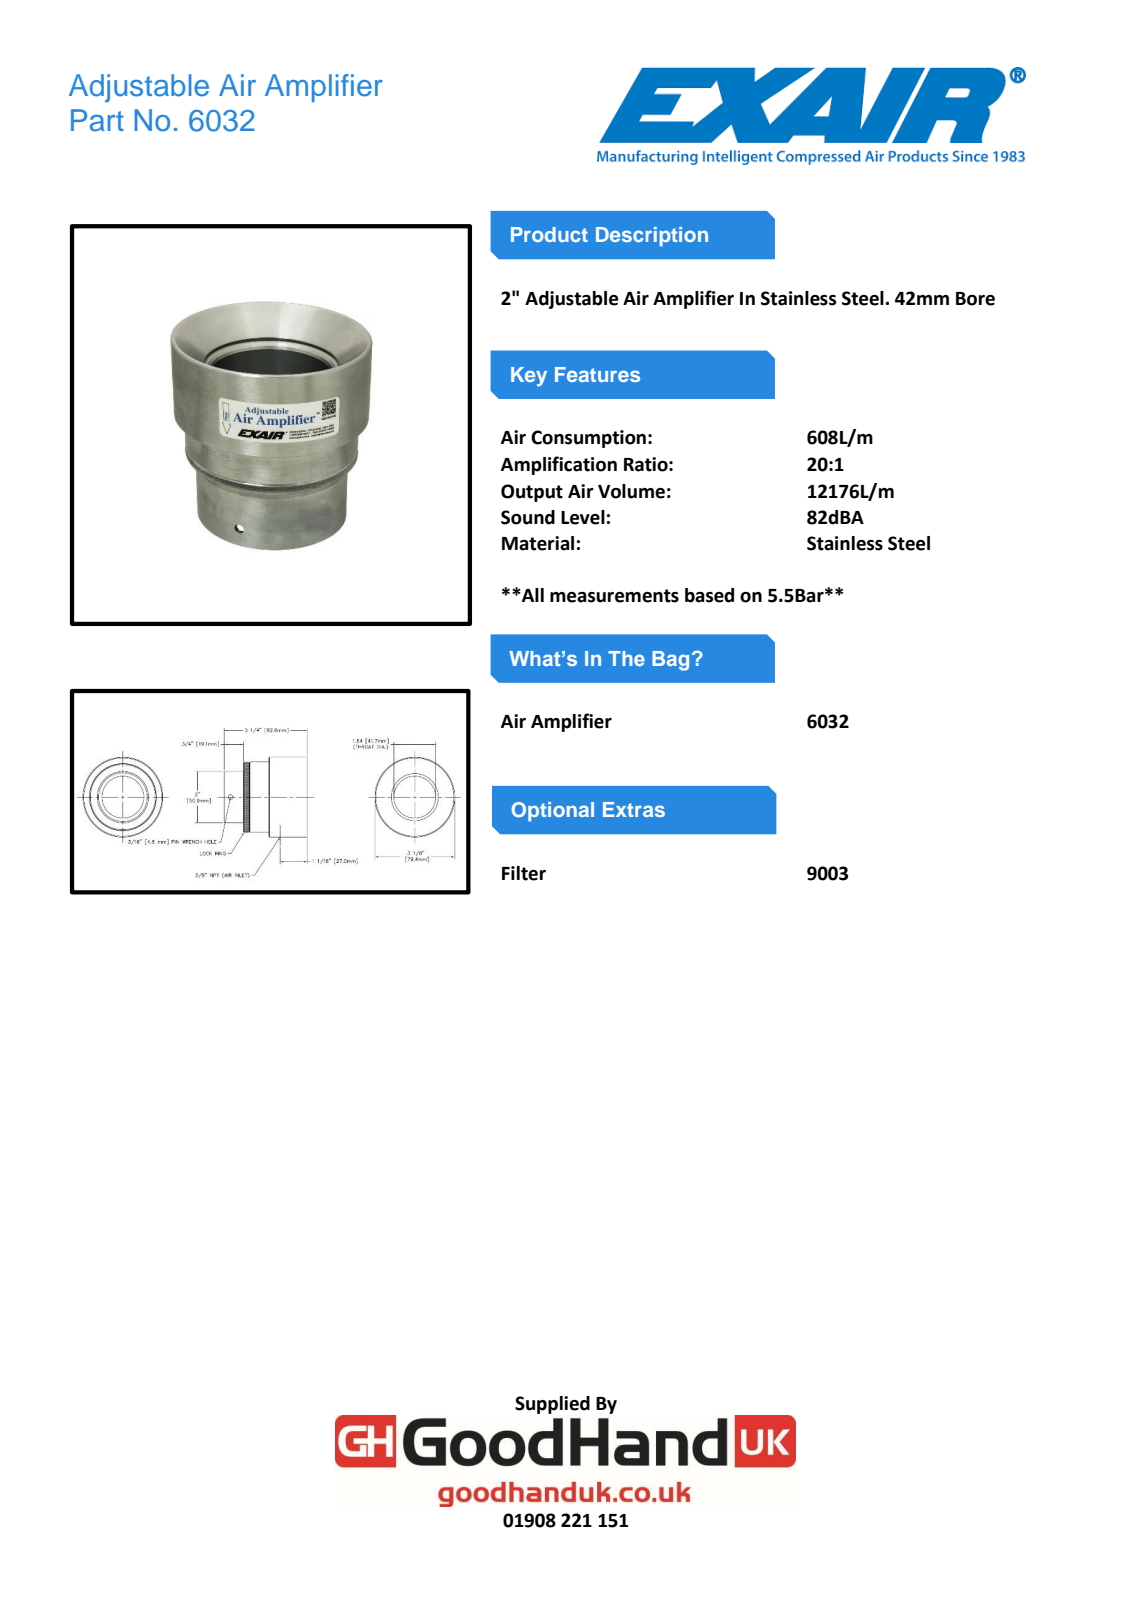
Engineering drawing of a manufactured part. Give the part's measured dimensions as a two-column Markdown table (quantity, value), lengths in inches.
| quantity | value |
| --- | --- |
| part name | 6032-3D; 6032-3D1; 6032-3D2; 6032-3D3 |
| STEP written by | Autodesk Inventor 2008 (AUTOMOTIVE_DESIGN) |
| units | inches |
| bodies | 3 solids, 35 faces (11 planar, 10 cylindrical, 14 other) |
| overall size | 3.25 × 3.125 × 3.125 |
| volume | 10.36 in³ |
| surface area | 87.77 in² |
| round holes (diameter × count) | 0.187 × 1, 2.249 × 1, 2.307 × 1 |
| round bosses / shafts (diameter × count) | 3.125 × 1, 2.75 × 1, 2.734 × 1, 2.375 × 1, 2.238 × 1, 2.005 × 1 |
| main face-to-face distances | 1.625, 0.25, 1.875, 0.75, 1, 0.875, 1.75, 2.625, 1.438, 0.688 |
